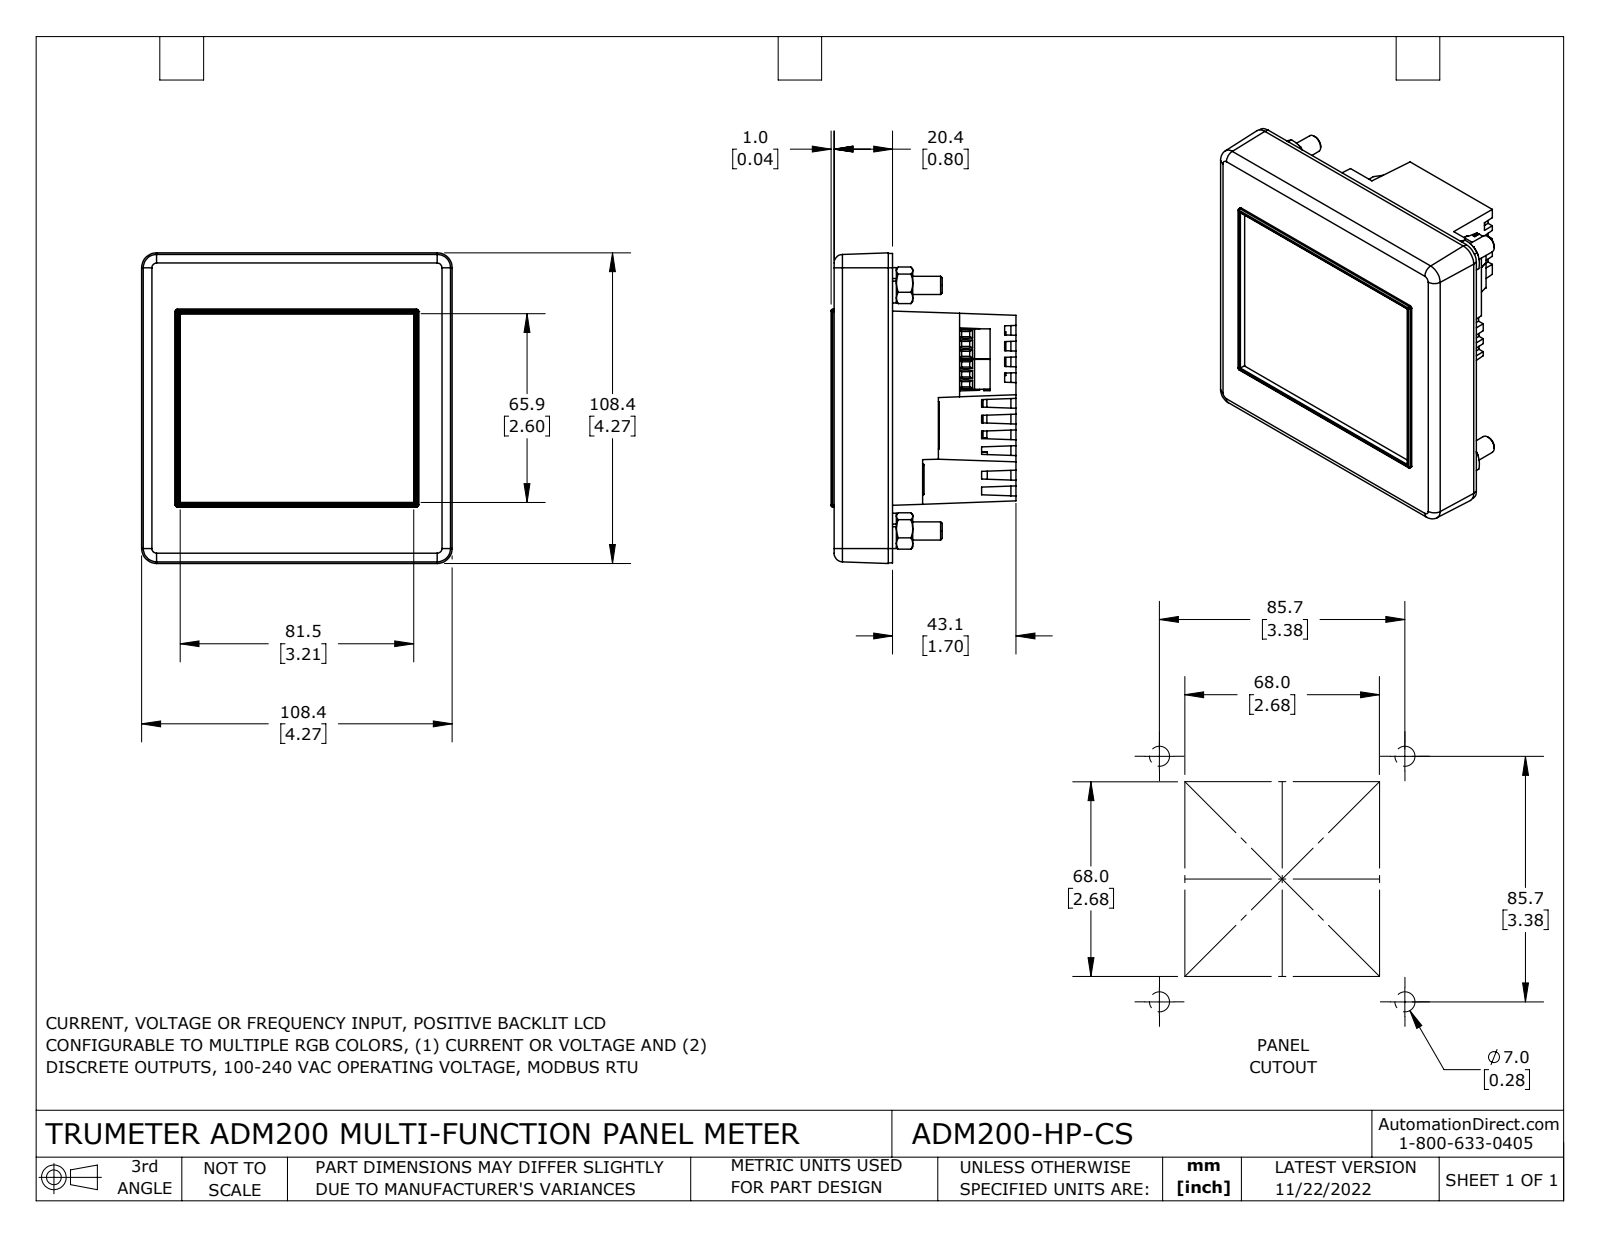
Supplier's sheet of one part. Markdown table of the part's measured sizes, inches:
| quantity | value |
| --- | --- |
| part name | ADM200-HP-CS |
| STEP written by | SolidWorks 2021 (CONFIG_CONTROL_DESIGN) |
| units | inches |
| bodies | 23 solids, 2059 faces (1384 planar, 290 cylindrical, 385 other) |
| overall size | 4.269 × 4.269 × 2.541 |
| volume | 7.808 in³ |
| surface area | 190.8 in² |
| round holes (diameter × count) | 0.071 × 9, 0.114 × 6, 0.118 × 5, 0.213 × 4, 0.25 × 4, 0.26 × 4, 0.295 × 4, 0.154 × 2 |
| round bosses / shafts (diameter × count) | 0.039 × 5, 0.487 × 4, 0.438 × 4, 0.024 × 4, 0.079 × 2 |
| partial cylindrical surfaces (radius × count) | 0.006 × 32, 0.02 × 30, 0.039 × 7, 0.016 × 4, 0.03 × 4, 0.118 × 4, 0.197 × 4, 0.004 × 2 |
| main face-to-face distances | 0.031, 0.635, 0.11, 0.073, 0.059, 0.079, 0.694, 3.395, 3.468, 0.047 |
| hole center spacings | 0.709, 3.228, 0.136, 0.293, 0.986, 1.417, 2.126, 2.399 |
